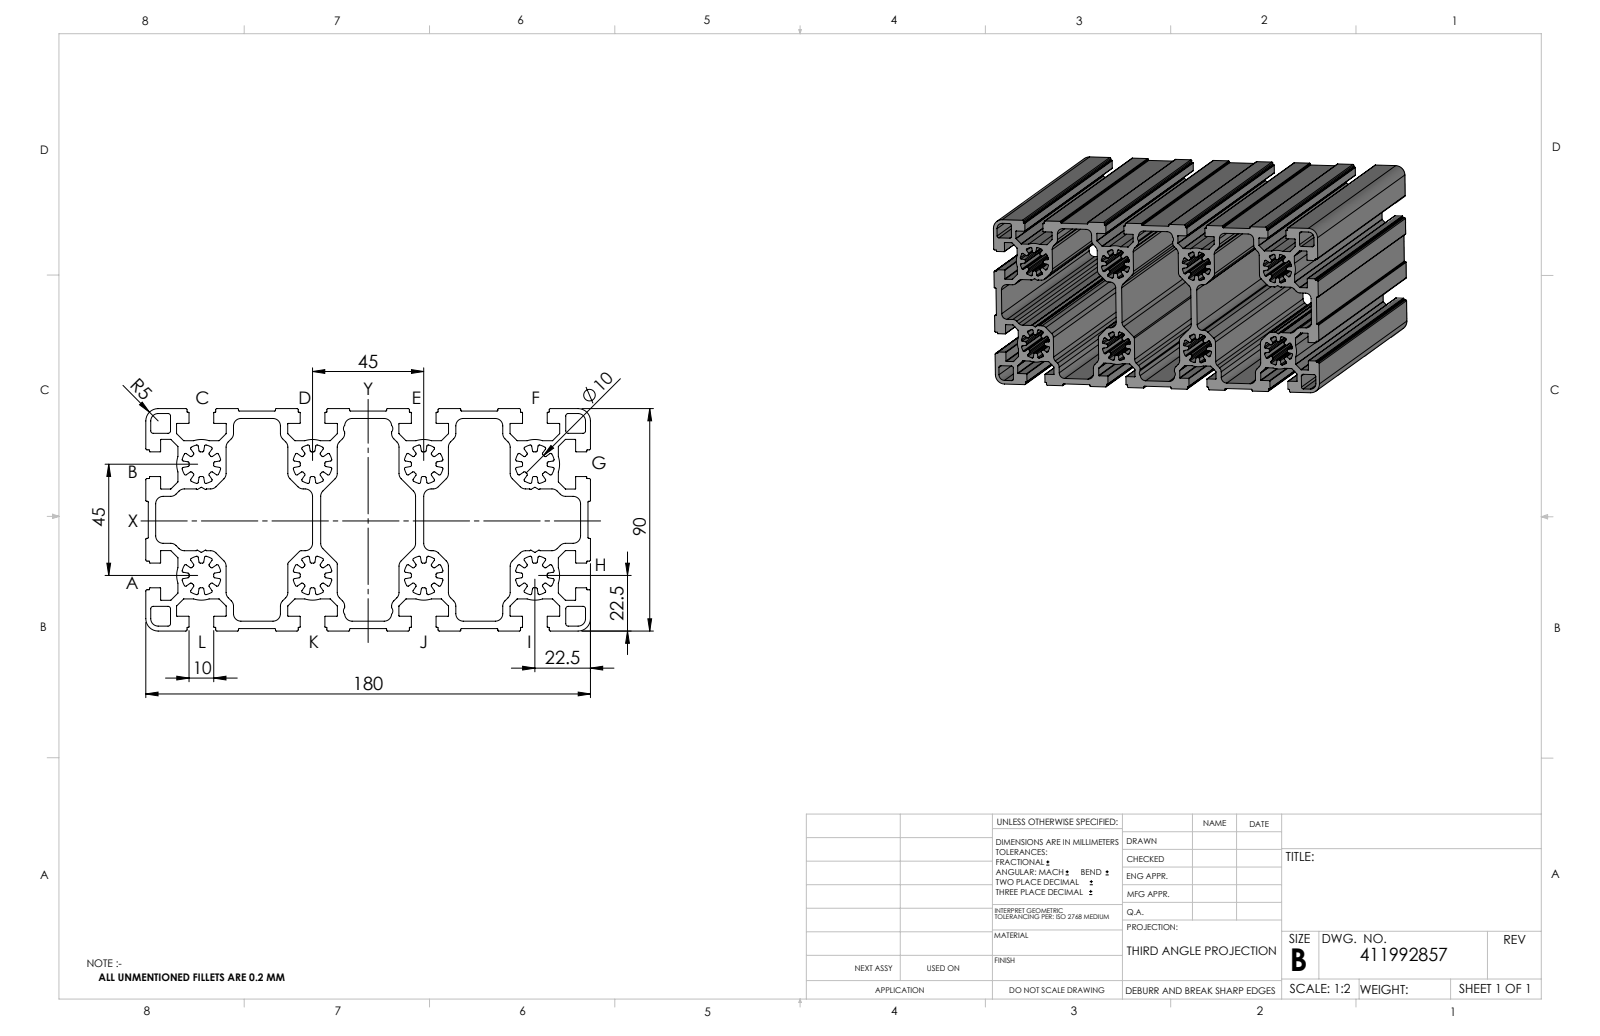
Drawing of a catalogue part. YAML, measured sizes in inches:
part_name: "411992857_c_1"
step_written_by: "SolidWorks 2014 (CONFIG_CONTROL_DESIGN)"
units: inches
bodies: {solids: 1, faces: 1256, planar: 458, cylindrical: 798, other: 0}
overall_size: [7.874, 7.087, 3.543]
volume: 51.62
surface_area: 804.7
partial_cylinders:
  - {radius: 0.02, count: 280}
  - {radius: 0.008, count: 164}
  - {radius: 0.118, count: 77}
  - {radius: 0.012, count: 32}
  - {radius: 0.039, count: 15}
  - {radius: 0.197, count: 12}
  - {radius: 0.315, count: 8}
  - {radius: 0.394, count: 8}
face_to_face_distances: [0.157, 3.15, 0.236, 0.079, 0.039, 0.118, 1.772, 0.197, 0.394, 3.543]
